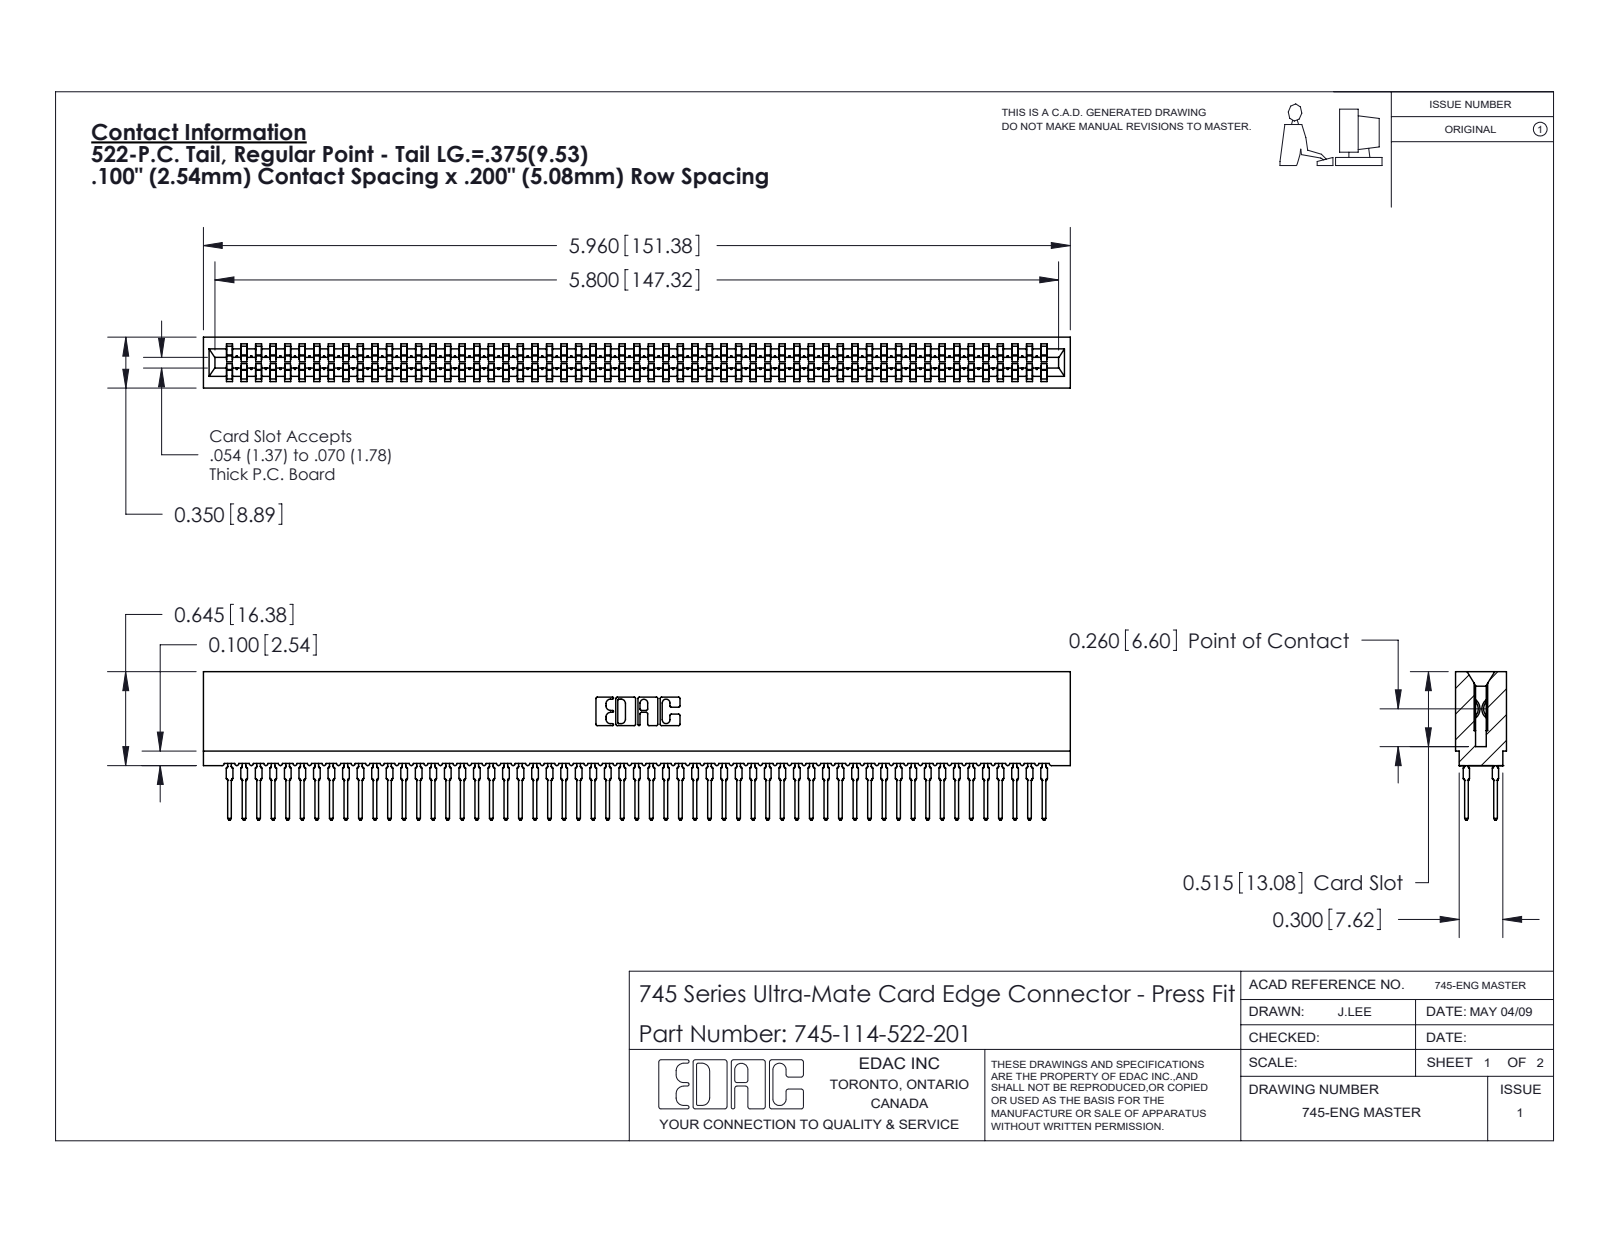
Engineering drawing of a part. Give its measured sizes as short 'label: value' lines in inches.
name: 745-114-522-201; 745-292-001_522; 745 Part_Insulator Option - 01
written by: SolidWorks 2020 (CONFIG_CONTROL_DESIGN)
unit: in
bodies: 115 solids, 10298 faces (5299 planar, 2035 cylindrical, 2964 other)
size: 5.96 × 1.021 × 0.35
volume: 0.834 in³; area: 44.2 in²
rounds: 228× R0.021, 114× R0.015, 22× R0.01, 8× R0.005, 8× R0.011, 6× R0.007, 6× R0.031, 3× R0.026
face distances: 0.35, 0.063, 0.287, 0.045, 0.305, 0.018, 0.243, 0.138, 0.212, 0.093
